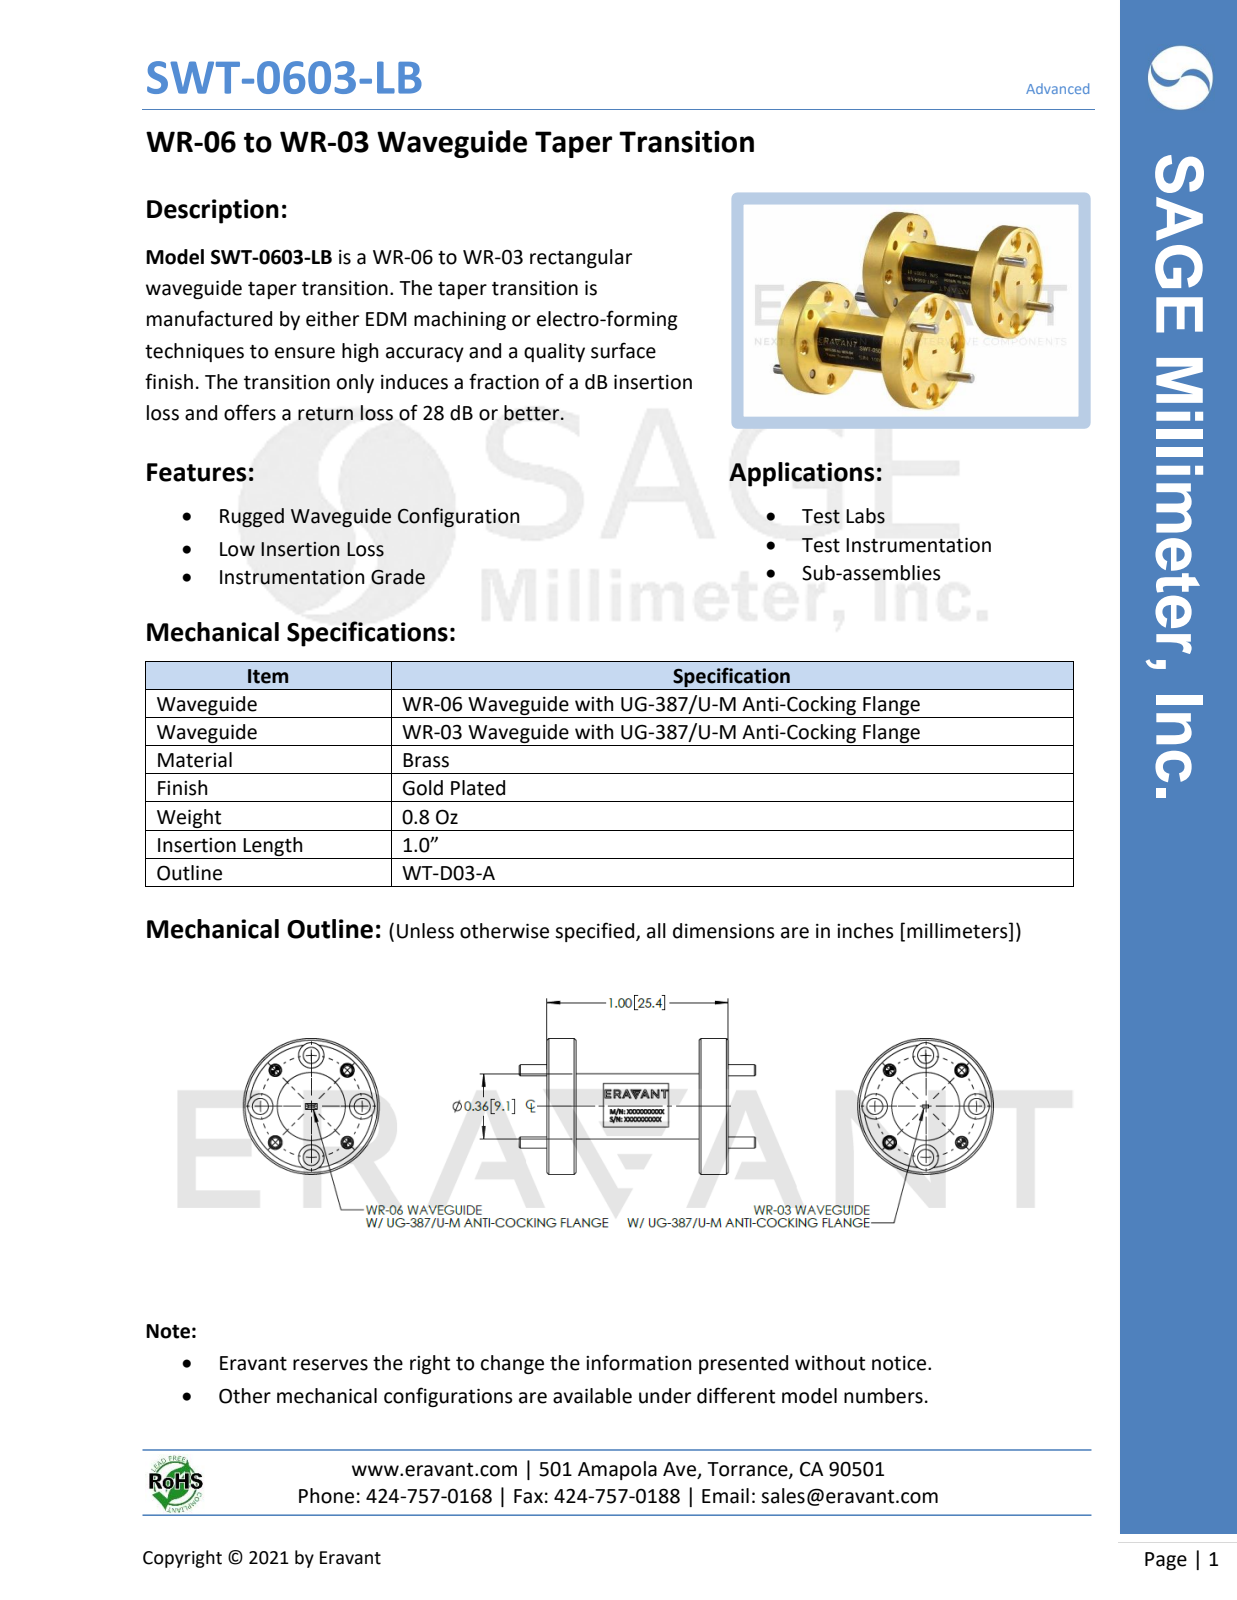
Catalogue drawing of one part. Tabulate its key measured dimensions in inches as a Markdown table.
| quantity | value |
| --- | --- |
| part name | SWT-0803-LB |
| STEP written by | SolidWorks 2021 (CONFIG_CONTROL_DESIGN) |
| units | inches |
| bodies | 5 solids, 148 faces (34 planar, 74 cylindrical, 40 other) |
| overall size | 1.305 × 0.75 × 0.75 |
| volume | 0.19 in³ |
| surface area | 3.865 in² |
| round holes (diameter × count) | 0.061 × 4, 0.067 × 4, 0.089 × 4, 0.14 × 4, 0.68 × 1 |
| round bosses / shafts (diameter × count) | 0.063 × 4, 0.75 × 1, 0.375 × 1, 0.36 × 1 |
| main face-to-face distances | 0.98, 0.02, 0.68, 0.82, 0.14, 0.14, 0.82, 0.96, 0.16, 0.84 |
| hole center spacings | 0.215, 0.52, 0.398, 0.281, 0.281, 0.563, 0.398, 0.216 |
